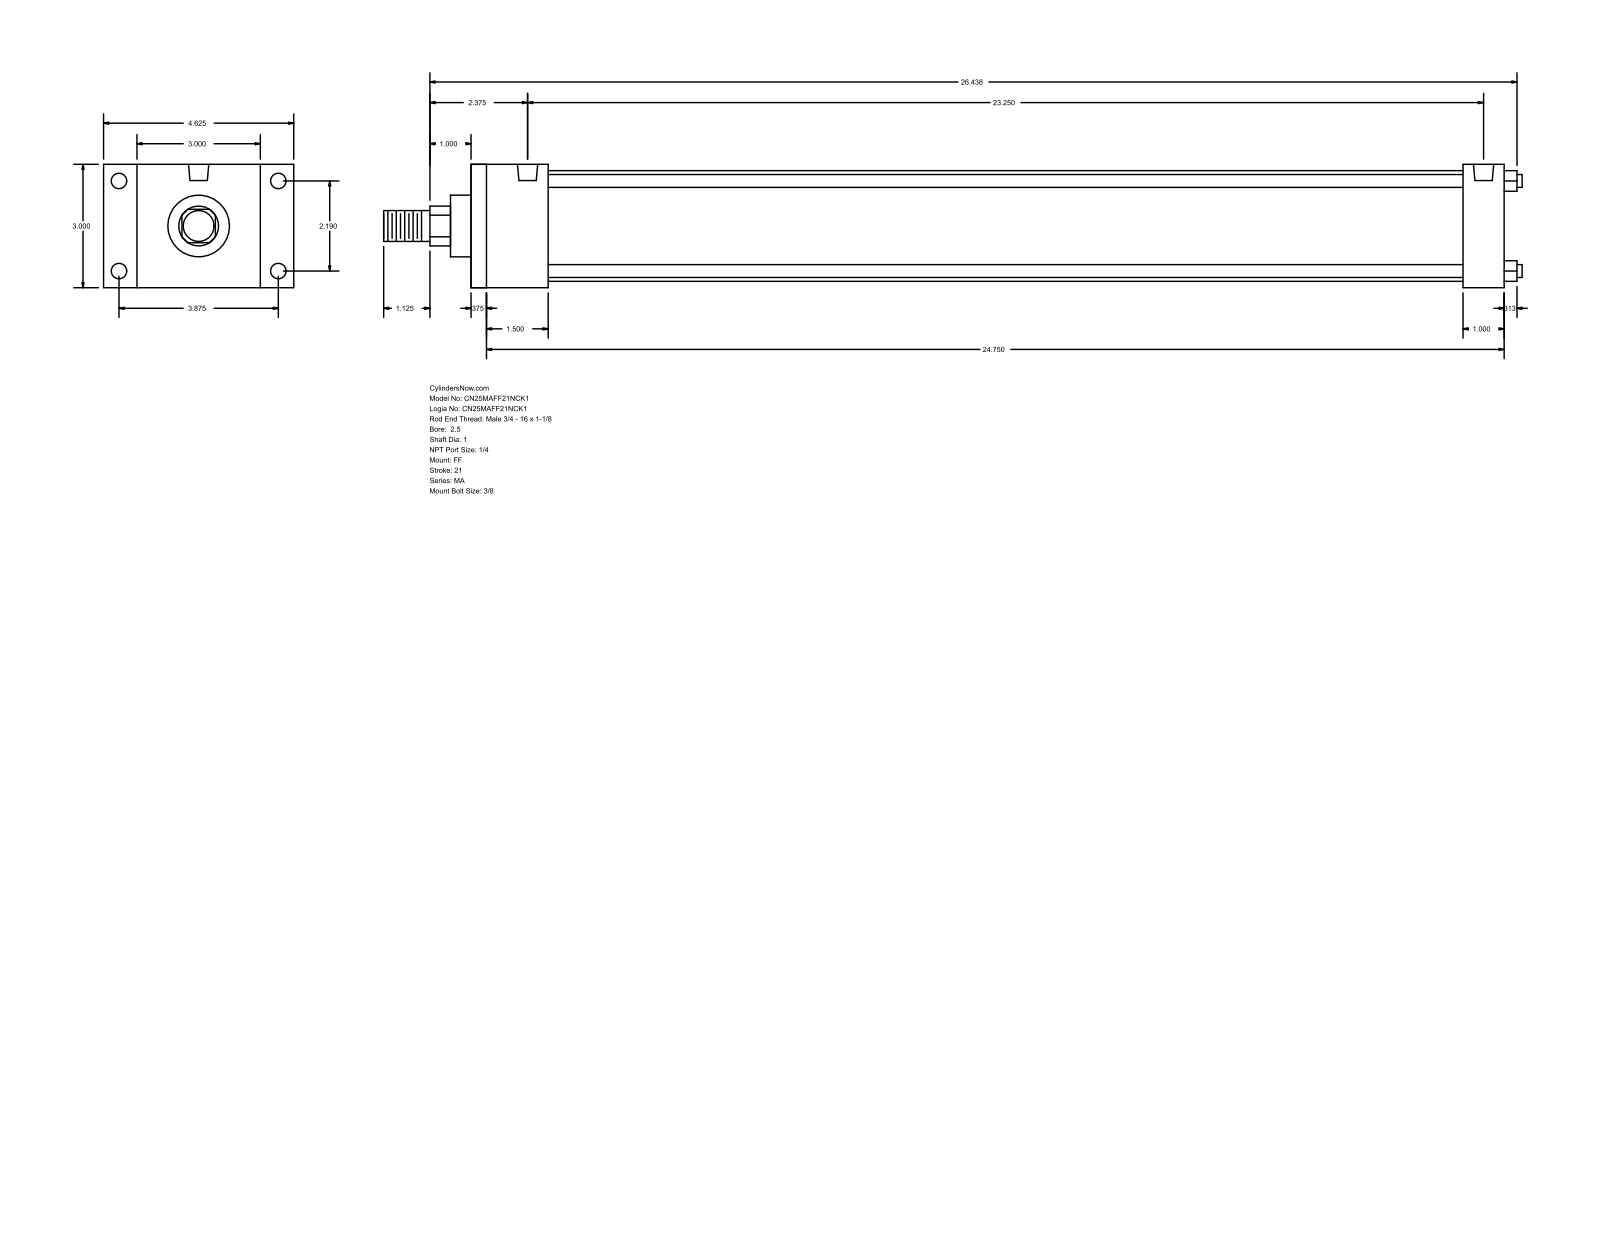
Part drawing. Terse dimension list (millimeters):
name: MA_FF__0250_1
written by: GSSL Pune (CONFIG_CONTROL_DESIGN)
unit: mm
bodies: 0 solids, 92 faces (64 planar, 28 cylindrical, 0 other)
size: 703.26 × 117.47 × 76.2
holes: 4× ⌀7.94, 4× ⌀9.53, 2× ⌀12.49
bosses: 4× ⌀7.94, 1× ⌀68.33, 1× ⌀38.1, 1× ⌀25.4, 1× ⌀19.05
rounds: 1× R12.29
face distances: 76.2, 638.18, 9.52, 628.66, 47.63, 612.77, 38.11, 603.25, 565.14, 590.55
hole spacings: 55.62, 98.42, 113.05, 590.55
